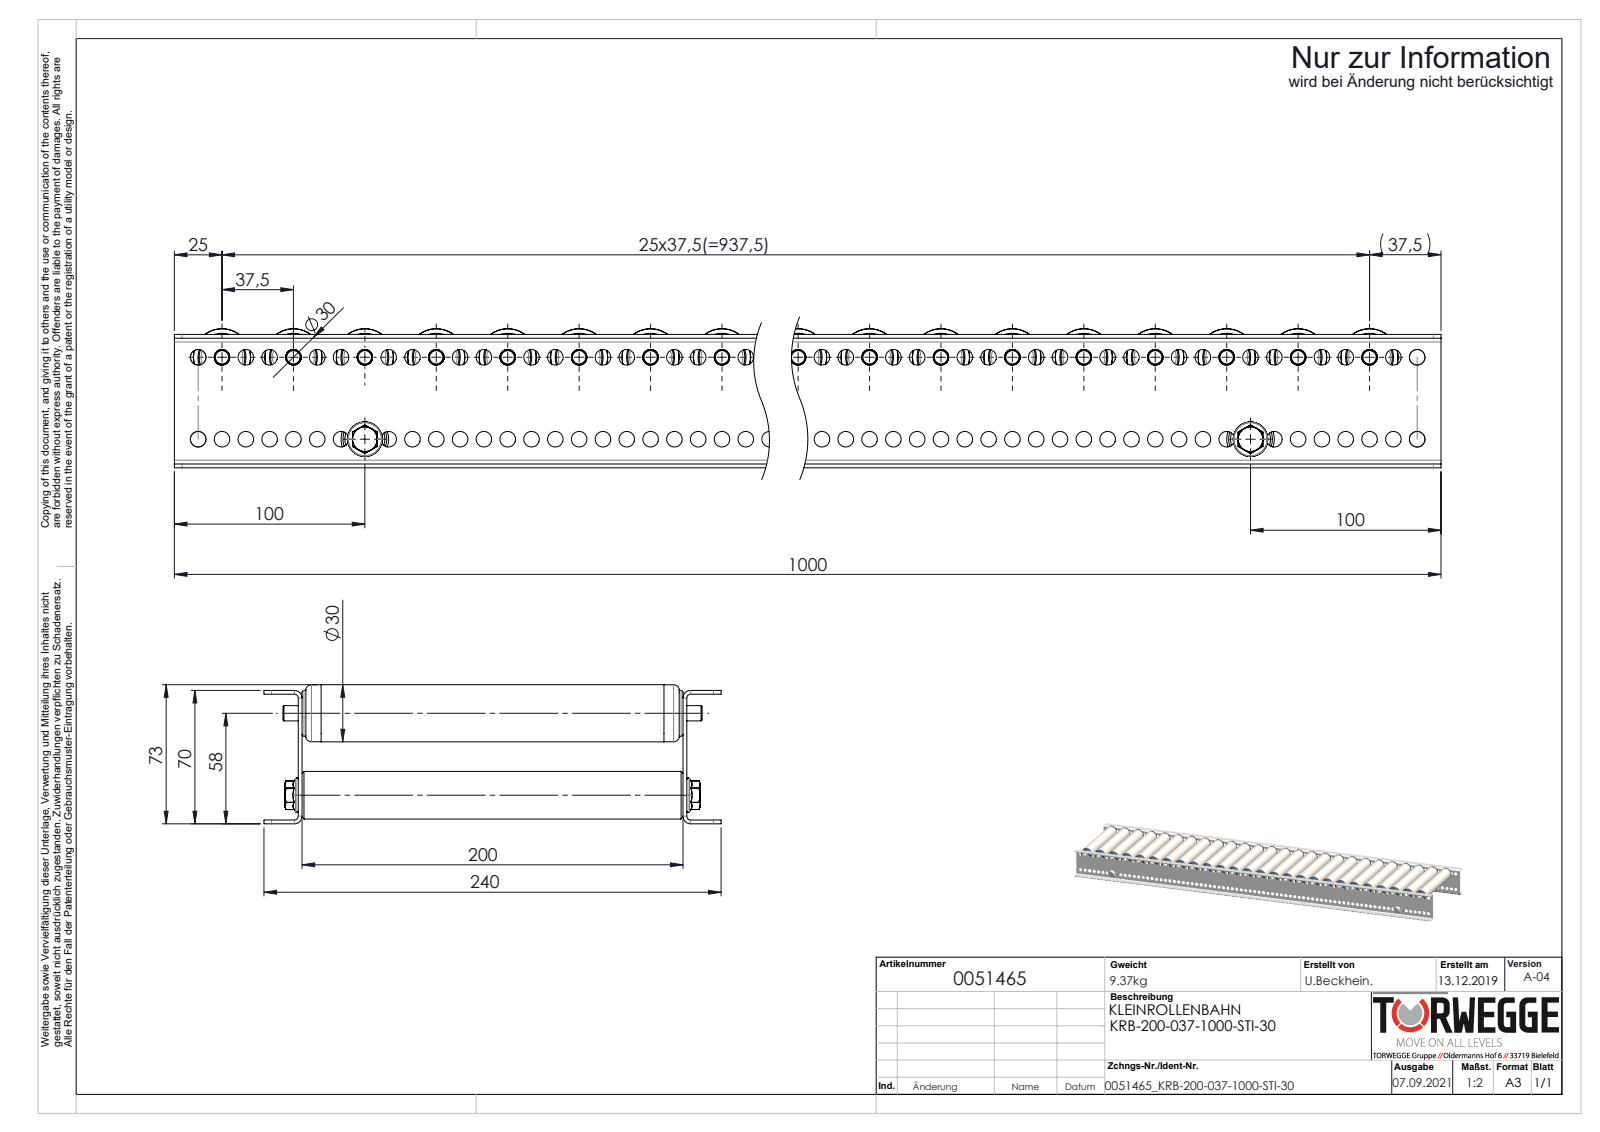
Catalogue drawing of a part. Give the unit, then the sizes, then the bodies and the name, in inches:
Units: inches
Overall size (bounding box): 39.37 × 9.449 × 2.874
Round holes (diameter × count): ⌀0.323 ×158, ⌀0.315 ×26, ⌀0.319 ×26, ⌀0.913 ×26, ⌀0.992 ×26, ⌀1.063 ×26, ⌀0.268 ×2, ⌀0.827 ×2
Round bosses / shafts (diameter × count): ⌀1.181 ×26, ⌀1.177 ×26, ⌀1.067 ×26, ⌀1.055 ×26, ⌀0.945 ×26, ⌀0.551 ×26, ⌀0.984 ×2, ⌀0.315 ×2
Partial cylindrical surfaces — rounded edges, fillets, slot ends (radius × count): R0.199 ×26, R0.157 ×8, R0.079 ×4
Main face-to-face distances: 0.079, 7.953, 7.874, 2.677, 8.031, 2.598, 2.756, 0.394, 7.48, 0.787
Hole centre spacings: 0.492, 0.984, 1.476, 1.969, 2.461, 2.953, 3.445, 3.937
Volume: 85.25 in³ · Surface area: 2 841 in²
Bodies: 168 solids, 6996 faces (2200 planar, 2768 cylindrical, 2028 other)
Part name (STEP PRODUCT): 0024176_Passscheibe_DIN988_8x14x1; 0040250_DRUCK-FEDER-8mm; 0039778-Achse-ST-Ø08-KFG_AL220-G-FA; KUT50-30x1,5-STI-A8-FA_KFG_S100903_KUT50-30x1,5-STI-A8-FA-EL=200 (+6 more)
STEP written by: SolidWorks 2020 (AUTOMOTIVE_DESIGN)
